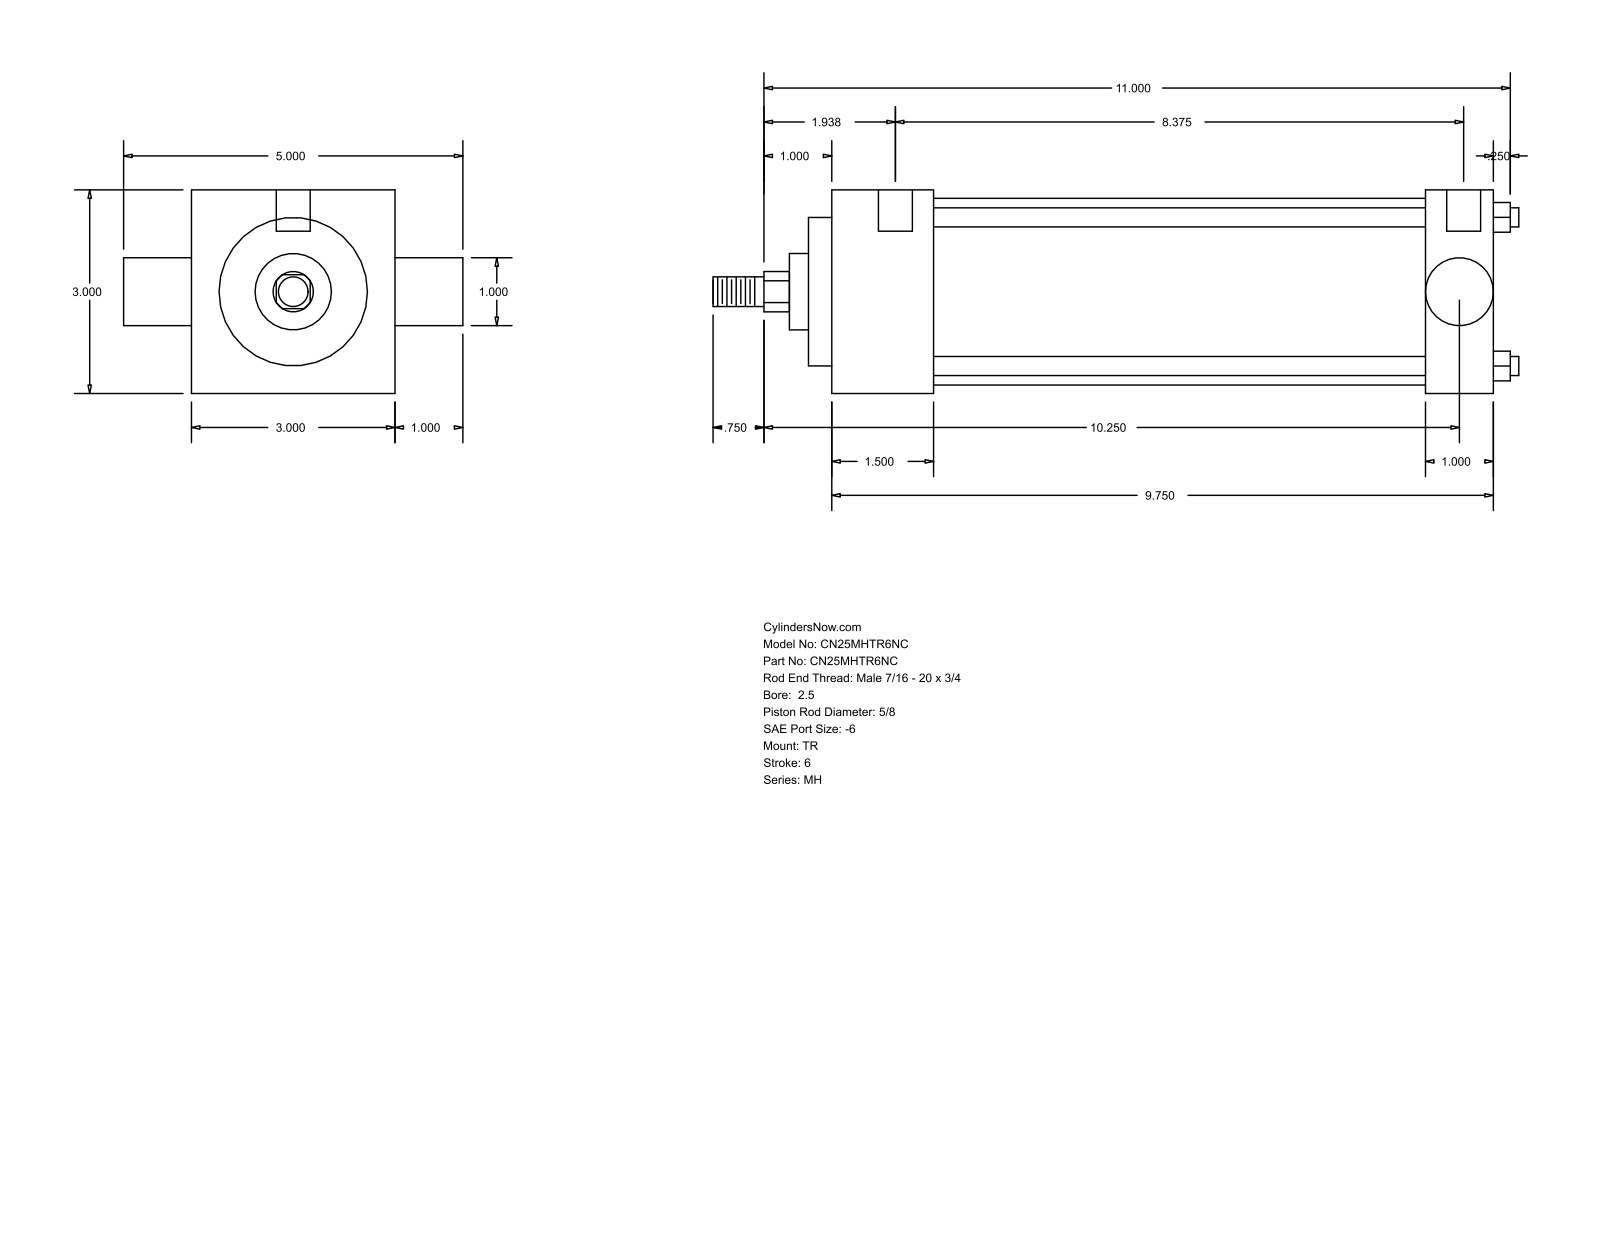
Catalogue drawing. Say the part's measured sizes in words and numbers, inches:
The part is named "MH_TR__0250_0.625". Its 3-D file was written by "GSSL Pune (CONFIG_CONTROL_DESIGN)". It is 0 solids with 86 faces: 61 planar, 25 cylindrical and 0 other. Overall it measures 11.875 by 5 by 3 inches. Round holes: 3 of diameter 0.219, 2 of diameter 0.5. Round bosses or shafts: 4 of diameter 0.281, 1 of diameter 2.75, 1 of diameter 2.187, 1 of diameter 1.125, 1 of diameter 0.998, 1 of diameter 0.625, 1 of diameter 0.437. Partial cylindrical surfaces (rounded edges, fillets, slot ends): 1 of radius 0.297. The main face-to-face distances are 3, 9.75, 1, 1.5, 8.25, 8.75, 7.25, 0.344, 1.844, 9.094. The hole center spacings are 0.125, 0.187, 8.375, 8.5, 8.563, 8.687.
